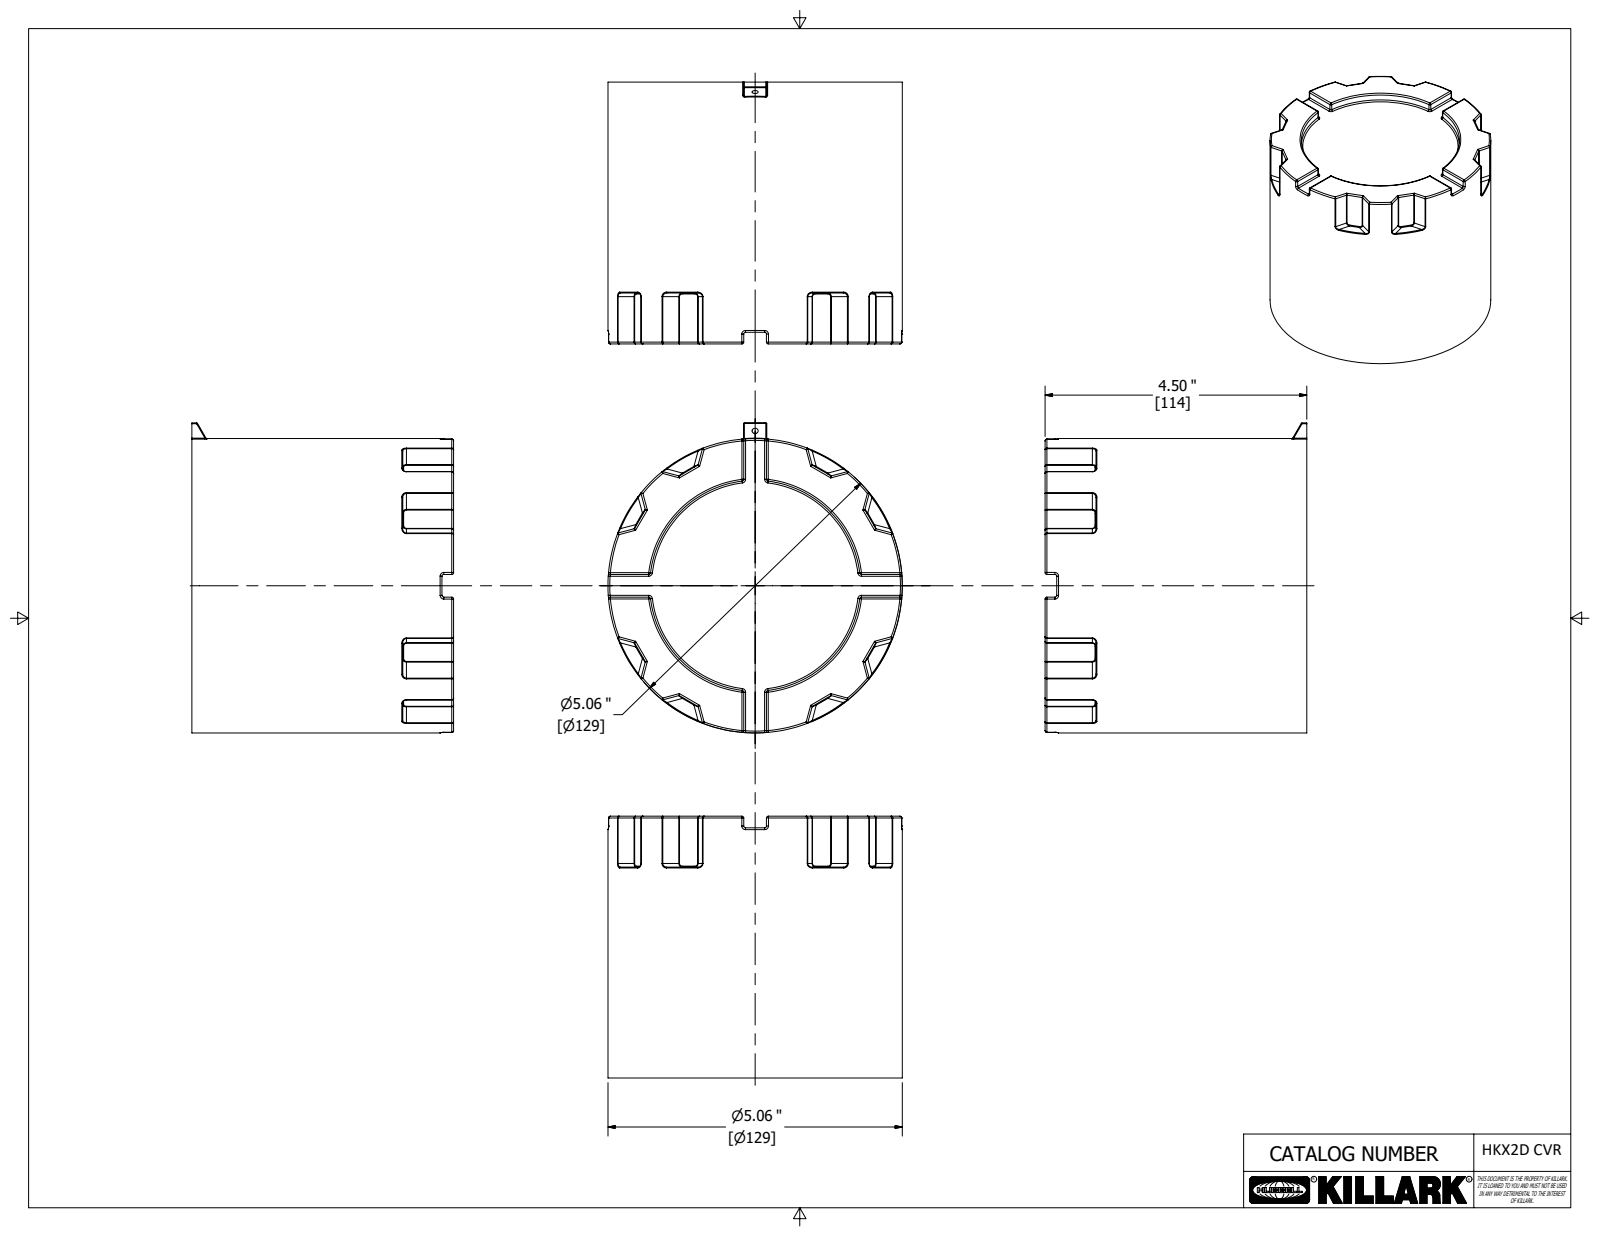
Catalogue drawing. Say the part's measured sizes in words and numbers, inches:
The part is named "51638ABAM for web". Its 3-D file was written by "Autodesk Inventor 2020 (AUTOMOTIVE_DESIGN)". It is 1 solid with 319 faces: 51 planar, 128 cylindrical and 140 other. Overall it measures 5.33 by 5.06 by 4.5 inches. Its volume is 29.36 cubic inches and its surface area 166 square inches. Round holes: 1 of diameter 0.104, 1 of diameter 3.624, 1 of diameter 4.2, 1 of diameter 4.39, 1 of diameter 4.86. Round bosses or shafts: 1 of diameter 5.06. Partial cylindrical surfaces (rounded edges, fillets, slot ends): 48 of radius 0.031, 47 of radius 0.016, 16 of radius 0.062. The main face-to-face distances are 0.25, 0.45, 0.2, 4.05, 4.3, 4.5, 2.969, 4.574, 2.97, 2.97.
